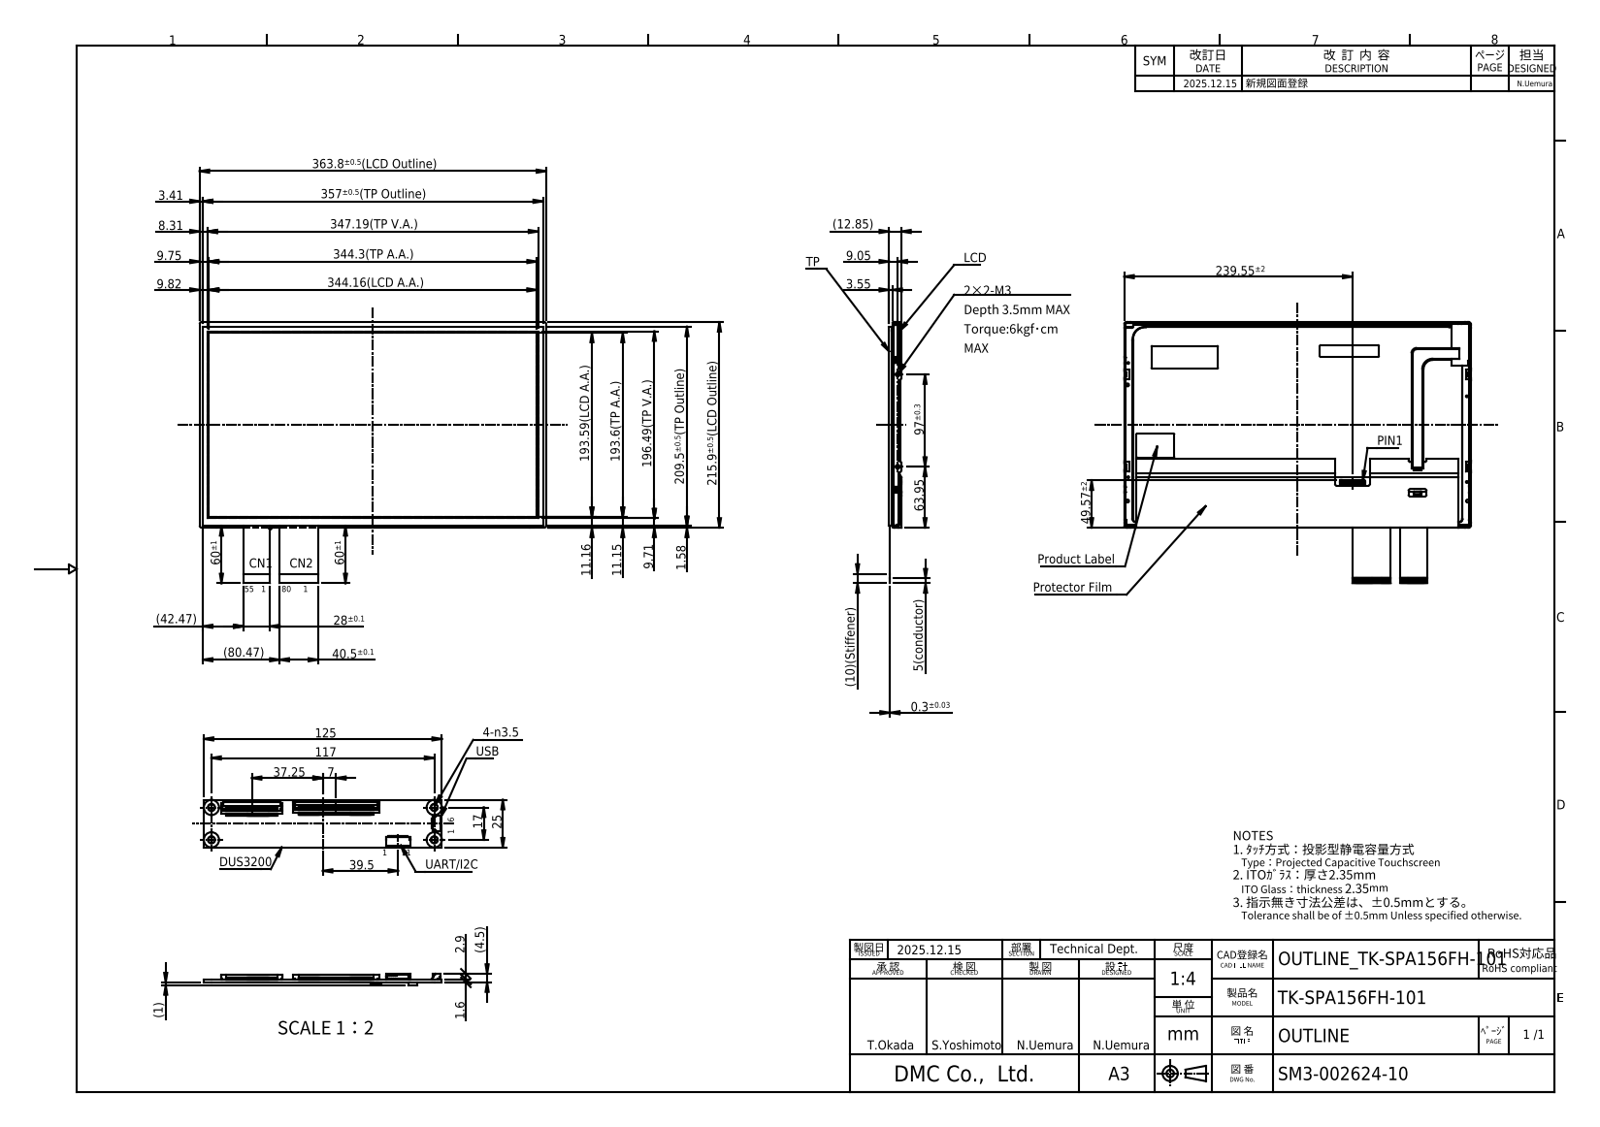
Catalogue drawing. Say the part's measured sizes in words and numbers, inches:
Its 3-D file was written by "Autodesk Inventor 2024 (AUTOMOTIVE_DESIGN)". It is 1 solid with 4190 faces: 2668 planar, 1232 cylindrical and 290 other. Overall it measures 14.323 by 10.8 by 0.506 inches. Its volume is 26.43 cubic inches and its surface area 610.5 square inches. Round holes: 4 of diameter 0.035, 4 of diameter 0.12, 3 of diameter 0.138, 3 of diameter 0.15, 2 of diameter 0.02, 2 of diameter 0.098, 2 of diameter 0.118, 2 of diameter 0.157. Round bosses or shafts: 4 of diameter 0.098, 3 of diameter 0.236, 3 of diameter 0.078, 2 of diameter 0.181. Partial cylindrical surfaces (rounded edges, fillets, slot ends): 137 of radius 0.039, 126 of radius 0.012, 94 of radius 0.02, 70 of radius 0.004, 62 of radius 0.008, 44 of radius 0.031, 23 of radius 0.024, 20 of radius 0.028. The main face-to-face distances are 0.382, 0.184, 0.198, 0.031, 0.413, 0.23, 0.089, 0.035, 0.093, 0.502. The hole center spacings are 3.819, 0.366, 0.382, 0.787, 0.788, 0.816, 0.856, 0.906.
